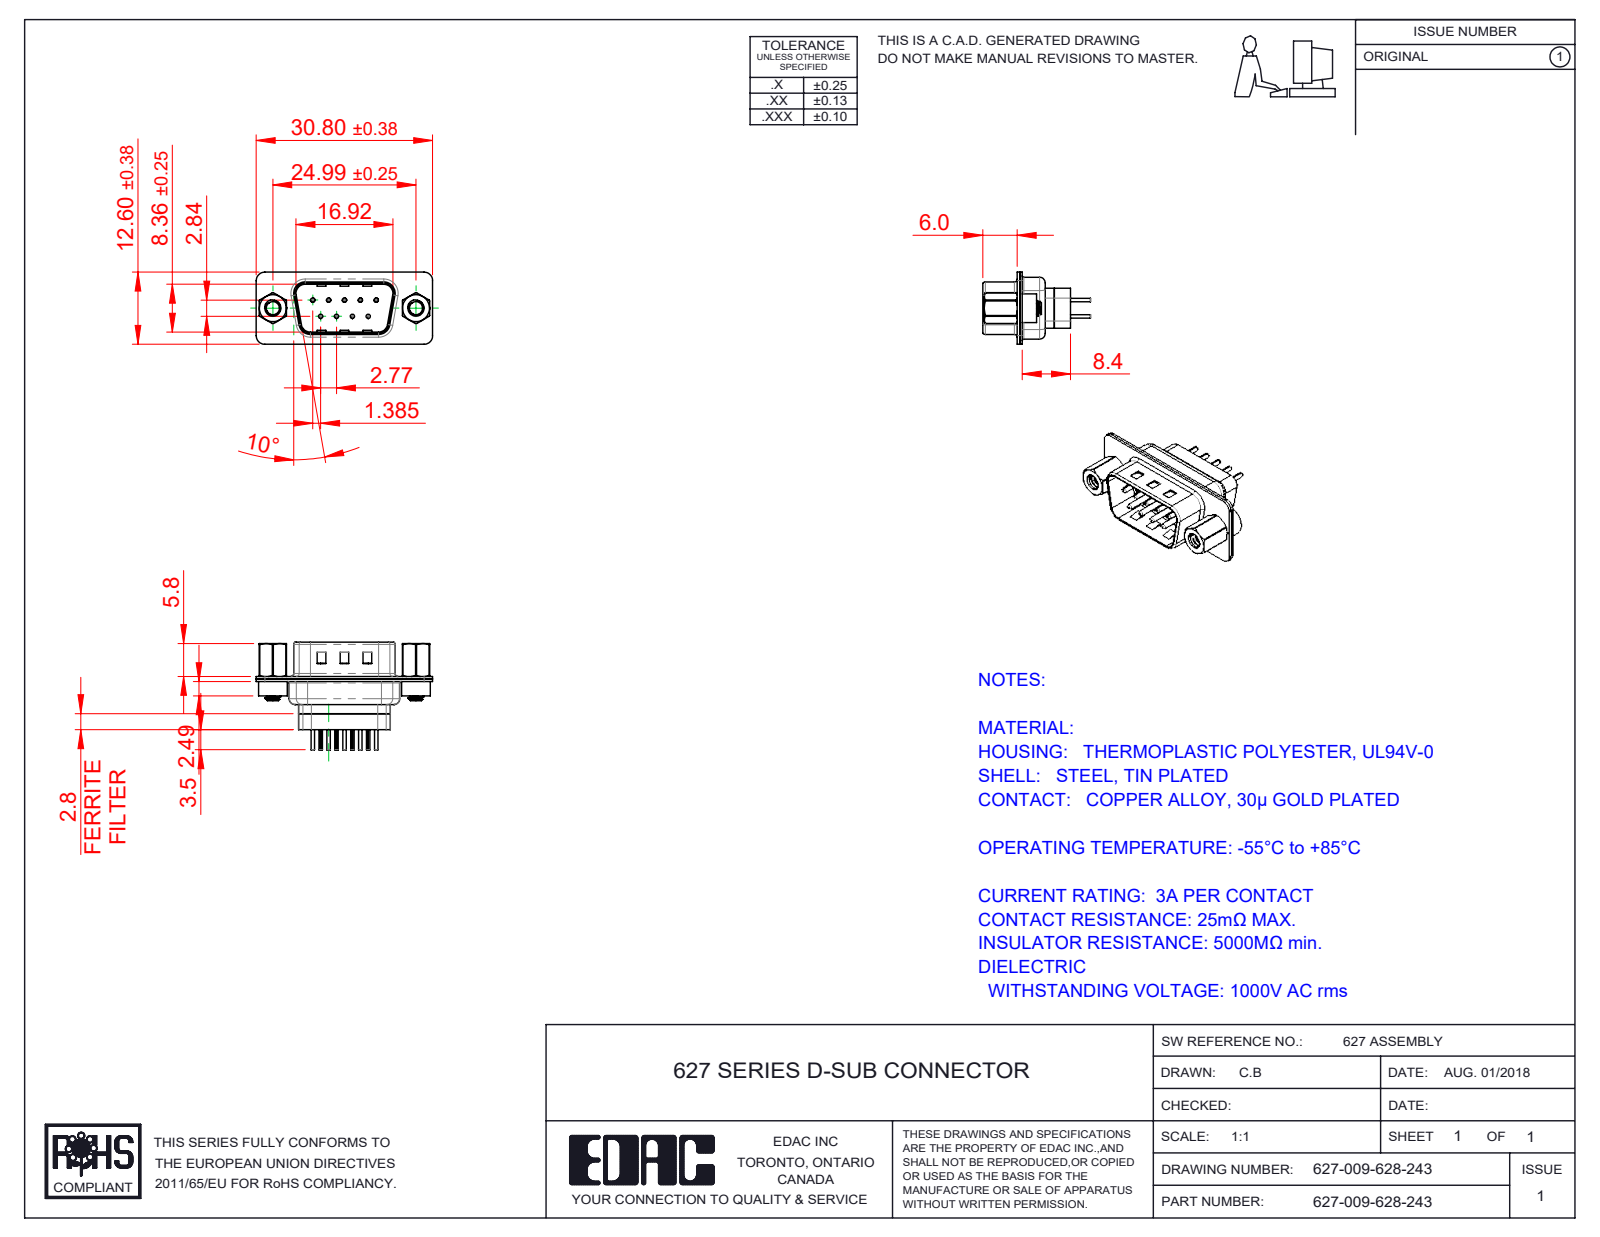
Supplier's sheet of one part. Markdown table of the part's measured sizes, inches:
| quantity | value |
| --- | --- |
| part name | 627 Contact Row 2_28L; 627 Shell Rear_09 Contacts; 627 Shell Front_09 Contacts; 627 4-40 Hex Standoff (+4 more) |
| STEP written by | SolidWorks 2020 (CONFIG_CONTROL_DESIGN) |
| units | inches |
| bodies | 17 solids, 1337 faces (351 planar, 555 cylindrical, 431 other) |
| overall size | 1.213 × 0.74 × 0.496 |
| volume | 0.108 in³ |
| surface area | 7.539 in² |
| round holes (diameter × count) | 0.008 × 9, 0.014 × 9, 0.043 × 9, 0.063 × 9, 0.089 × 2, 0.09 × 2, 0.157 × 2, 0.189 × 2 |
| round bosses / shafts (diameter × count) | 0.079 × 9, 0.059 × 9, 0.03 × 9, 0.024 × 9, 0.197 × 2, 0.193 × 2, 0.11 × 2 |
| partial cylindrical surfaces (radius × count) | 0.004 × 18, 0.059 × 18, 0.079 × 12, 0.02 × 8, 0.063 × 8, 0.01 × 4, 0.024 × 4, 0.026 × 4 |
| main face-to-face distances | 0.016, 0.018, 0.035, 0.256, 0.238, 0.22, 0.032, 0.377, 0.331, 0.055 |
| hole center spacings | 0.124, 0.109, 0.218, 0.198, 0.198, 0.327, 0.294, 0.295 |
